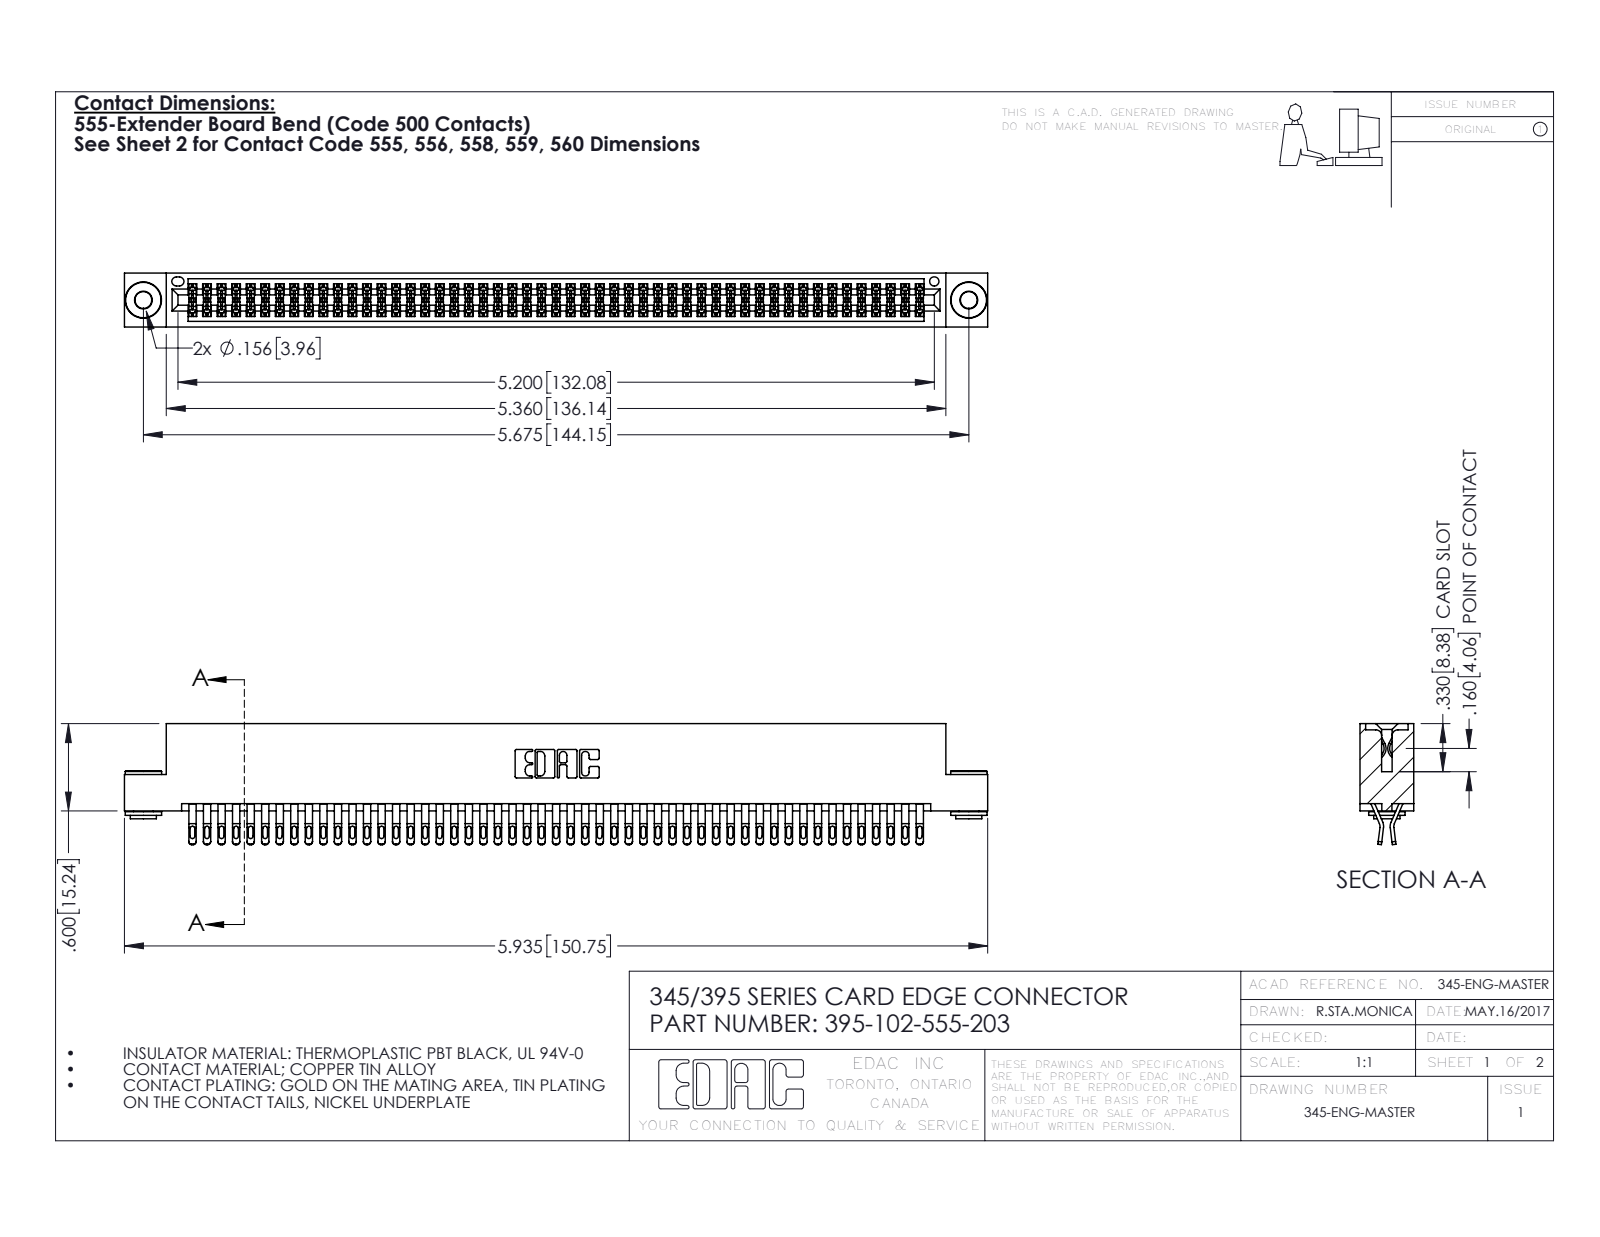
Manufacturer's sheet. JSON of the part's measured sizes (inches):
{"part_name": "345-292-001_555 Tail; 345 Part_Flush Mounting Lugs - 0.156 Dia-TH; 395-102-555-203; 345-250-002_345-250-002-102", "step_written_by": "SolidWorks 2016 (CONFIG_CONTROL_DESIGN)", "units": "inches", "bodies": {"solids": 105, "faces": 5876, "planar": 3252, "cylindrical": 2616, "other": 8}, "overall_size": [5.935, 0.832, 0.37], "volume_in3": 0.918, "surface_area_in2": 36.65, "round_holes": [[0.116, 2], [0.156, 2], [0.064, 1]], "round_bosses_or_shafts": [[0.25, 2], [0.18, 2], [0.136, 2]], "partial_cylinders_radius": [[0.016, 255], [0.02, 204], [0.006, 153], [0.01, 22], [0.007, 6], [0.031, 6], [0.026, 3], [0.01, 2]], "face_to_face_distances": [0.072, 0.298, 0.025, 0.2, 0.37, 0.098, 0.272, 0.225, 0.175, 0.149], "hole_center_spacings": [0.27, 5.439, 5.675]}
